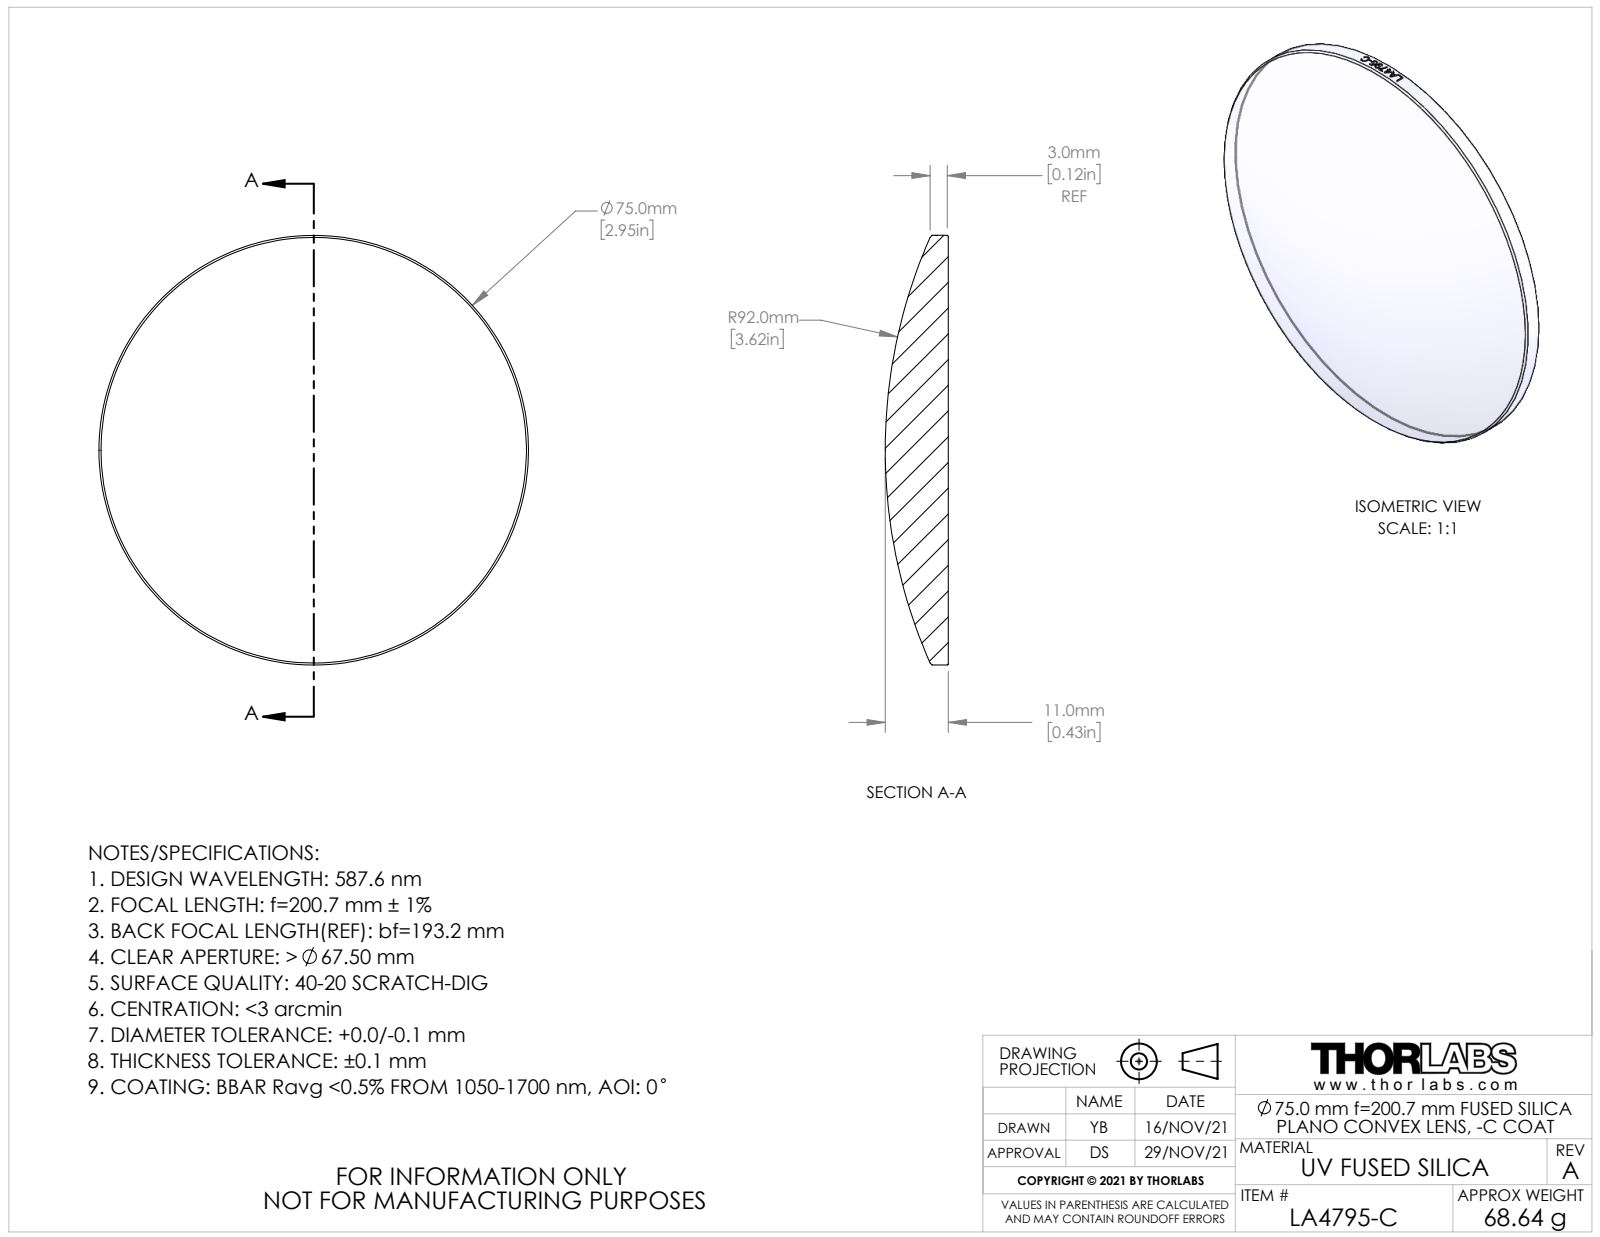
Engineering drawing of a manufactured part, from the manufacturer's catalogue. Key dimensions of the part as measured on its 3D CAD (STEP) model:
Part name (STEP PRODUCT): CTN018153; CTN018087-E0W
STEP written by: SolidWorks 2018 (AUTOMOTIVE_DESIGN)
Units: millimetres
Bodies: 1 solid, 20 faces (1 planar, 13 cylindrical, 6 other)
Overall size (bounding box): 75 × 75 × 10.99
Volume: 31 157 mm³ · Surface area: 9 702 mm²
Round bosses / shafts (diameter × count): ⌀75 ×1
